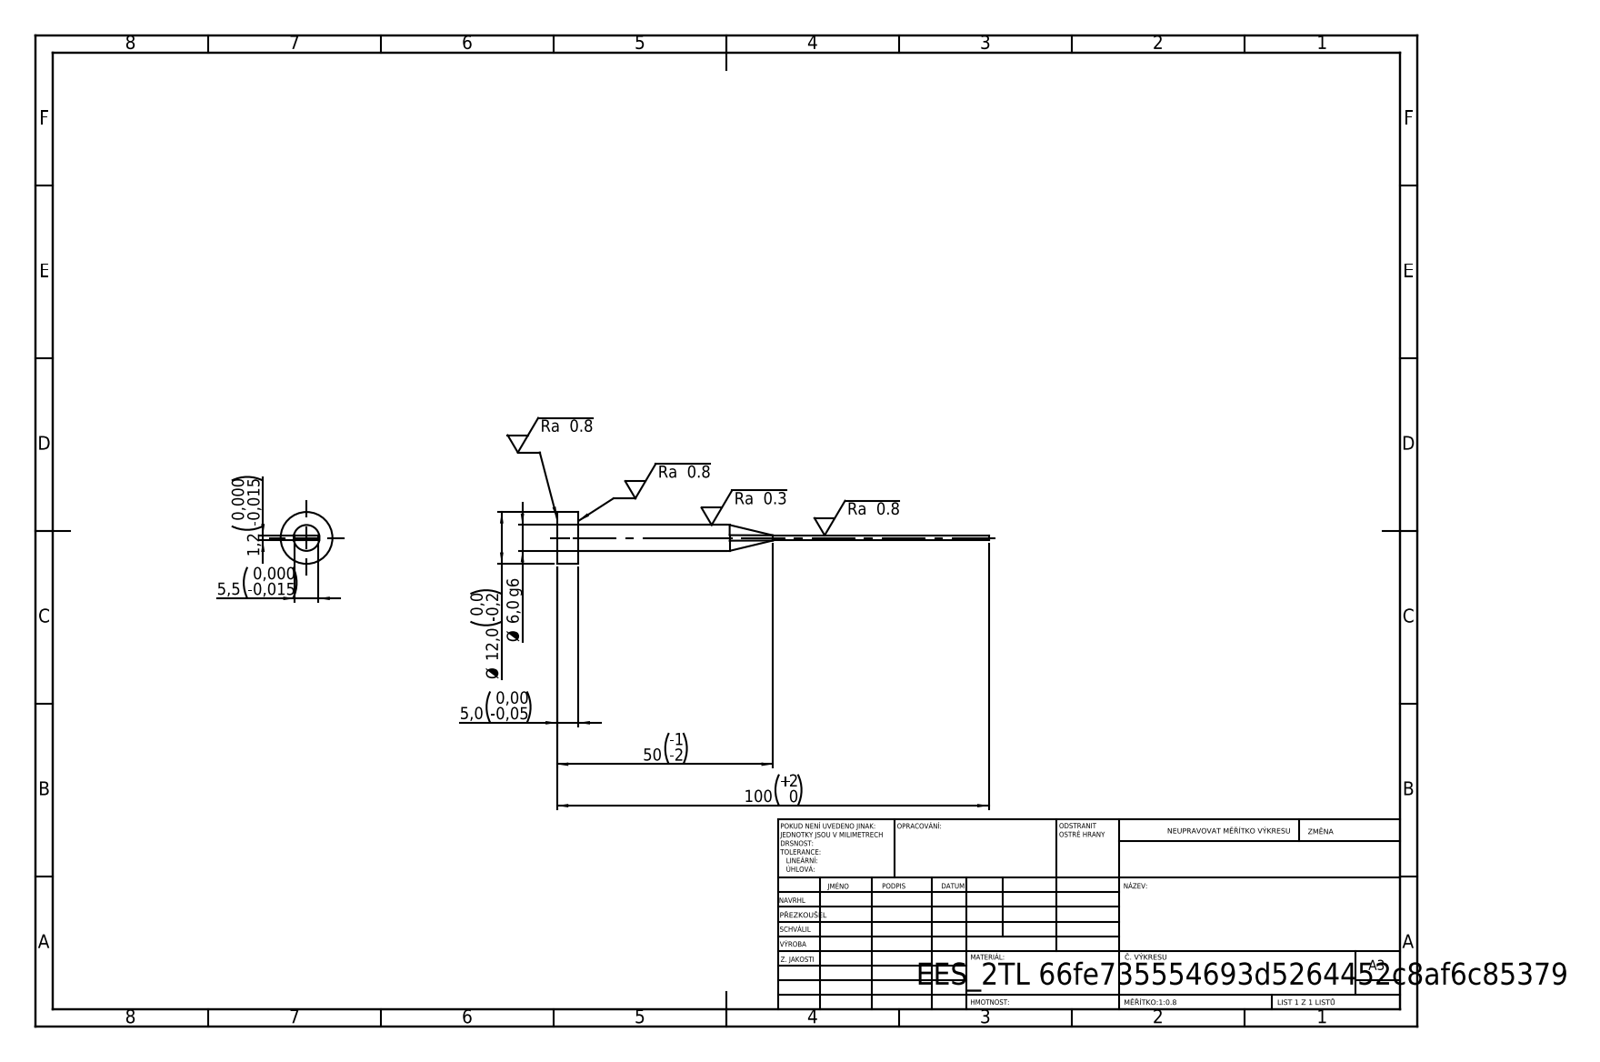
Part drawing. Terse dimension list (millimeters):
written by: SolidWorks 2019 (CONFIG_CONTROL_DESIGN)
unit: mm
bodies: 1 solid, 15 faces (7 planar, 4 cylindrical, 4 other)
size: 100 × 12 × 12
volume: 2 051 mm³; area: 1 879 mm²
bosses: 1× ⌀12, 1× ⌀6
face distances: 1.2, 5, 5.5, 100, 95
